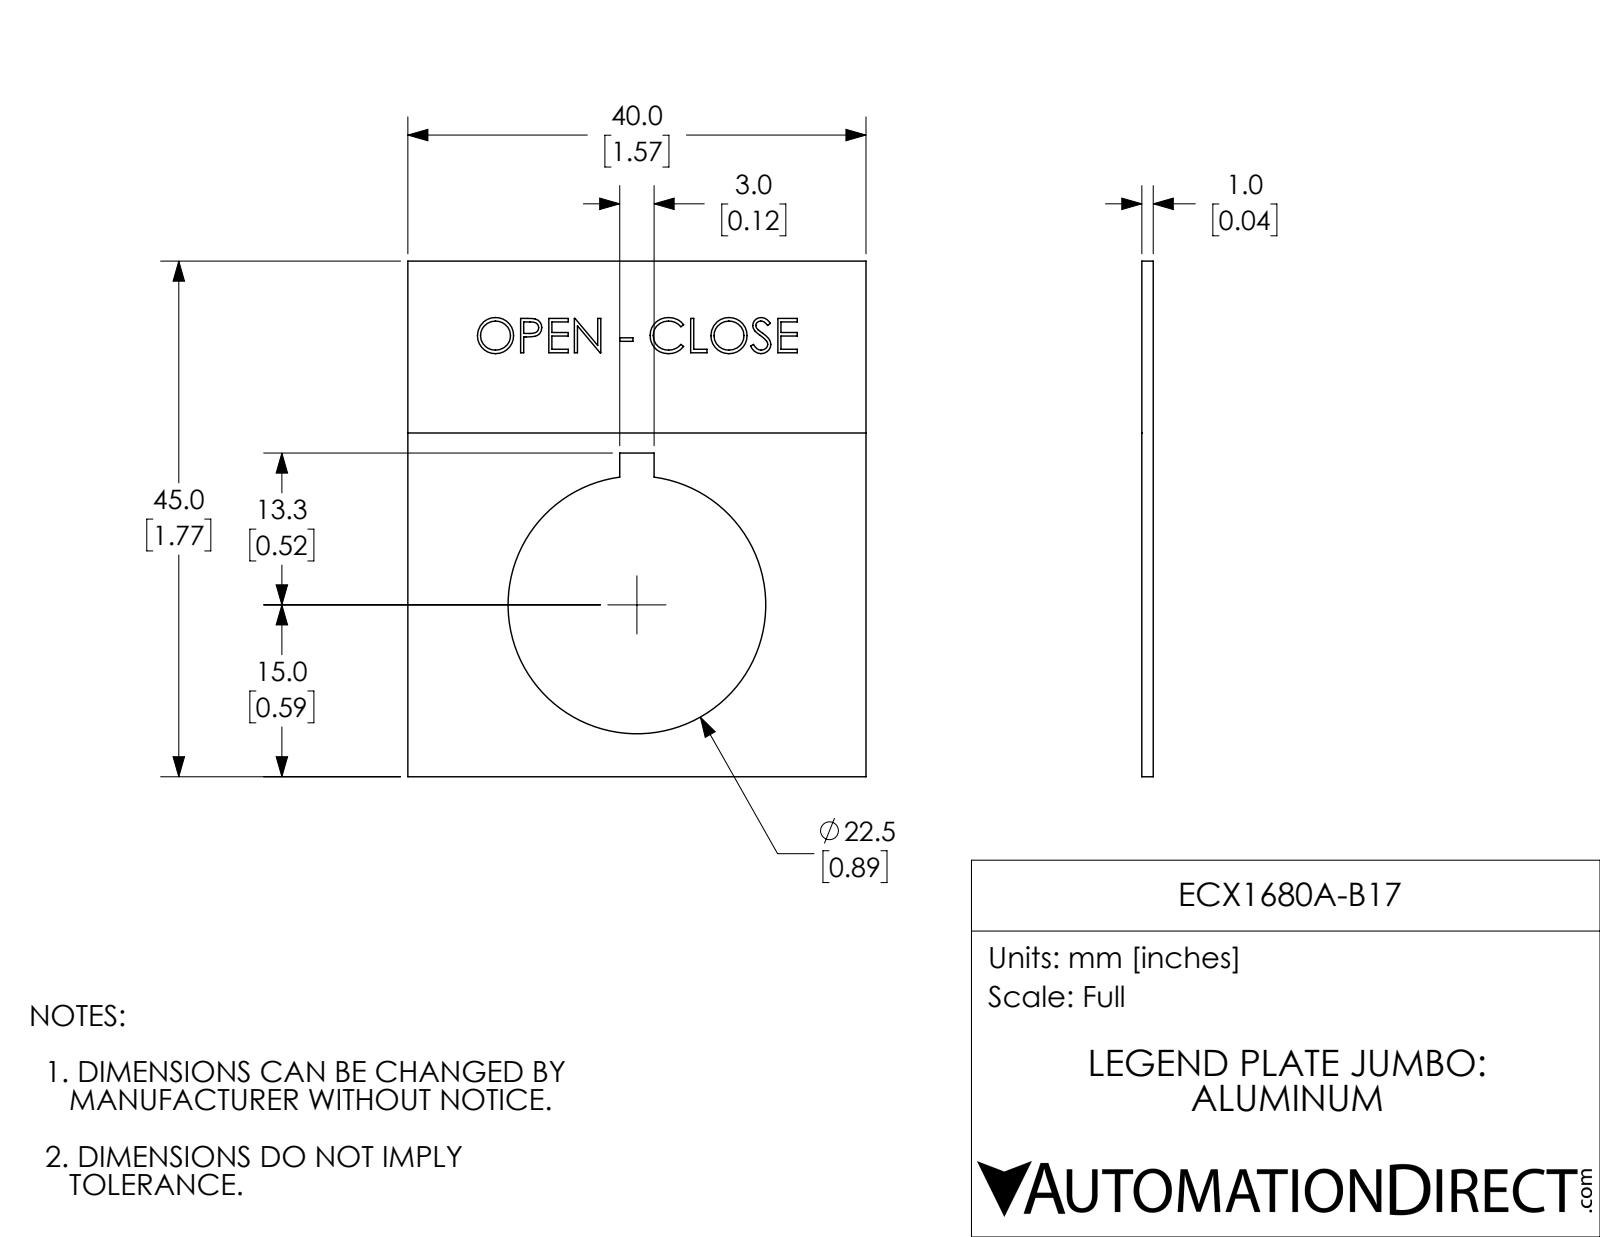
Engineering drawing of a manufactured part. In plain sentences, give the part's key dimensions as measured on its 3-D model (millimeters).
The part is named "ECX1680A-B17". Its 3-D file was written by "SolidWorks 2017 (AUTOMOTIVE_DESIGN)". It is 1 solid with 129 faces: 80 planar, 3 cylindrical and 46 other. Overall it measures 45 by 40 by 1 millimeters. Its volume is 1 393 cubic millimeters and its surface area 3 038 square millimeters. Round holes: 1 of diameter 22.5. The main face-to-face distances are 1, 0.99, 40, 45, 18.5, 21.5, 28.25, 16.75, 3, 30.
